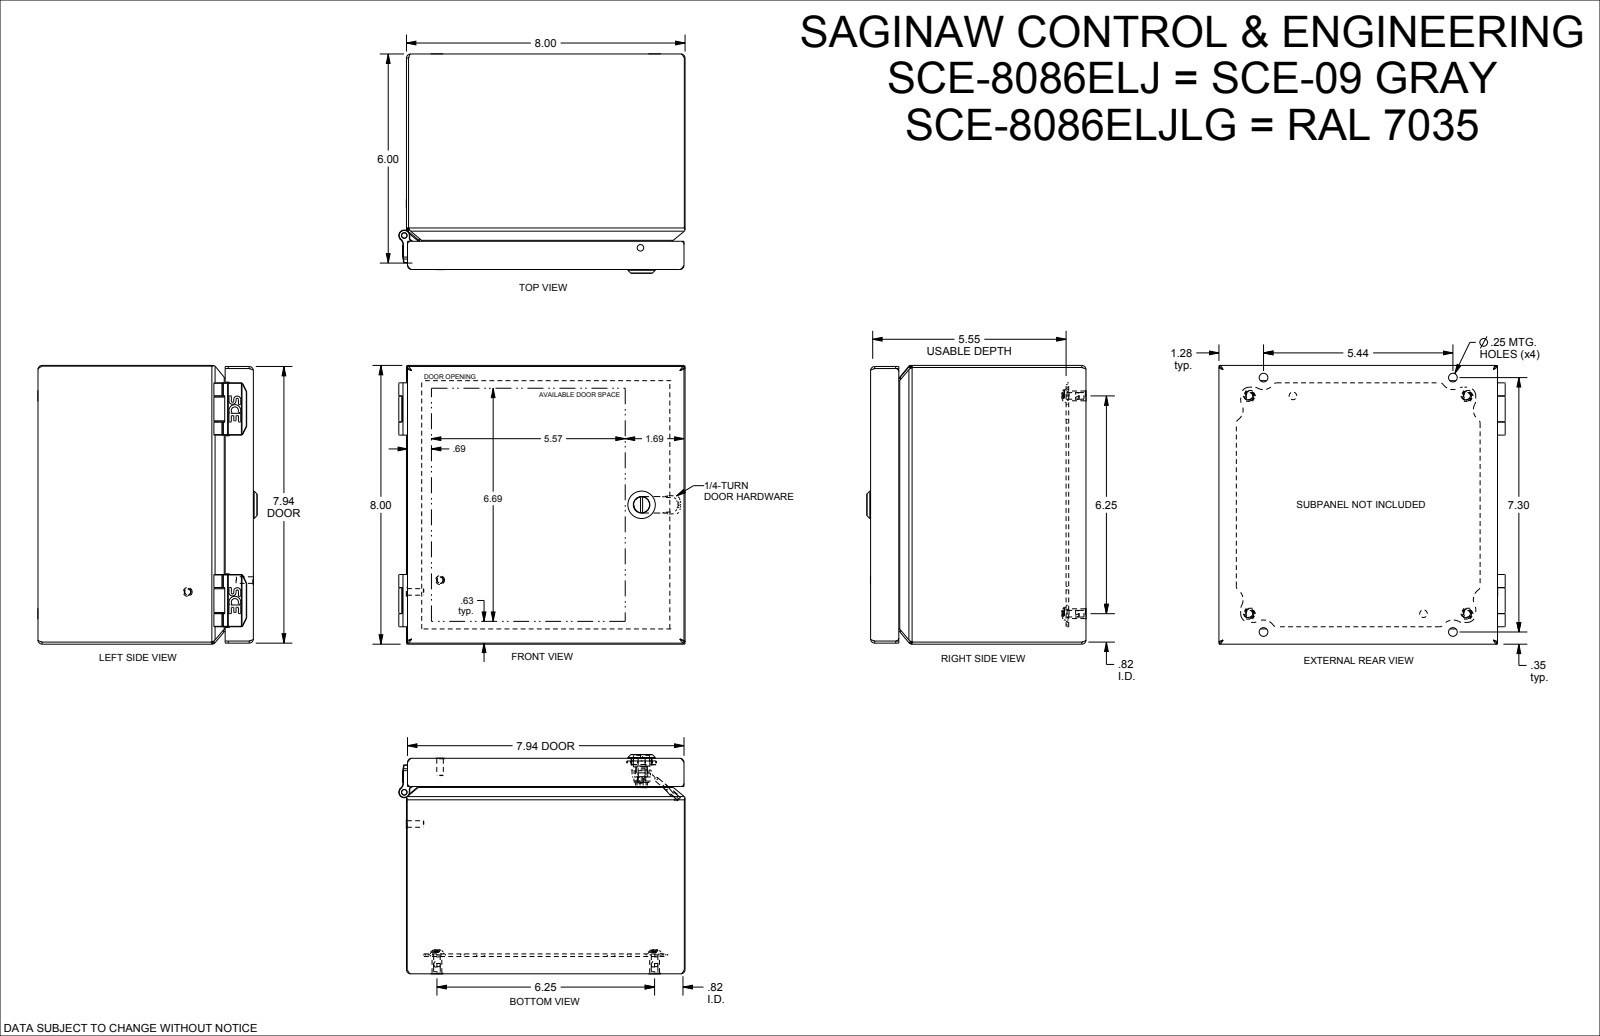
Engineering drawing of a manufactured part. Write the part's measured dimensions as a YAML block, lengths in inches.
part_name: "SCE-8086ELJLG"
step_written_by: "SolidWorks 2019 (CONFIG_CONTROL_DESIGN)"
units: inches
bodies: {solids: 0, faces: 2654, planar: 858, cylindrical: 764, other: 1032}
overall_size: [8.22, 8, 6.296]
round_holes:
  - {diameter: 0.25, count: 8}
  - {diameter: 0.19, count: 4}
  - {diameter: 0.284, count: 4}
  - {diameter: 0.479, count: 4}
  - {diameter: 0.02, count: 2}
  - {diameter: 0.1, count: 2}
  - {diameter: 0.174, count: 2}
  - {diameter: 0.196, count: 2}
  - {diameter: 0.218, count: 2}
  - {diameter: 0.266, count: 2}
  - {diameter: 0.158, count: 1}
  - {diameter: 0.187, count: 1}
round_bosses_or_shafts:
  - {diameter: 0.188, count: 6}
  - {diameter: 0.373, count: 4}
  - {diameter: 0.28, count: 4}
  - {diameter: 0.17, count: 4}
  - {diameter: 0.16, count: 4}
  - {diameter: 0.135, count: 4}
  - {diameter: 0.108, count: 4}
  - {diameter: 0.26, count: 2}
partial_cylinders:
  - {radius: 0.106, count: 132}
  - {radius: 0.005, count: 131}
  - {radius: 0.008, count: 32}
  - {radius: 0.01, count: 26}
  - {radius: 0.025, count: 24}
  - {radius: 0.03, count: 24}
  - {radius: 0.06, count: 22}
  - {radius: 0.013, count: 21}
face_to_face_distances: [0.06, 7.94, 0.06, 7.88, 8, 6.124, 6.065, 6.185, 6.125, 0.571]
hole_center_spacings: [0.664, 5.868, 6.25, 6.787, 8.948, 0.994, 1.25, 3.148]
